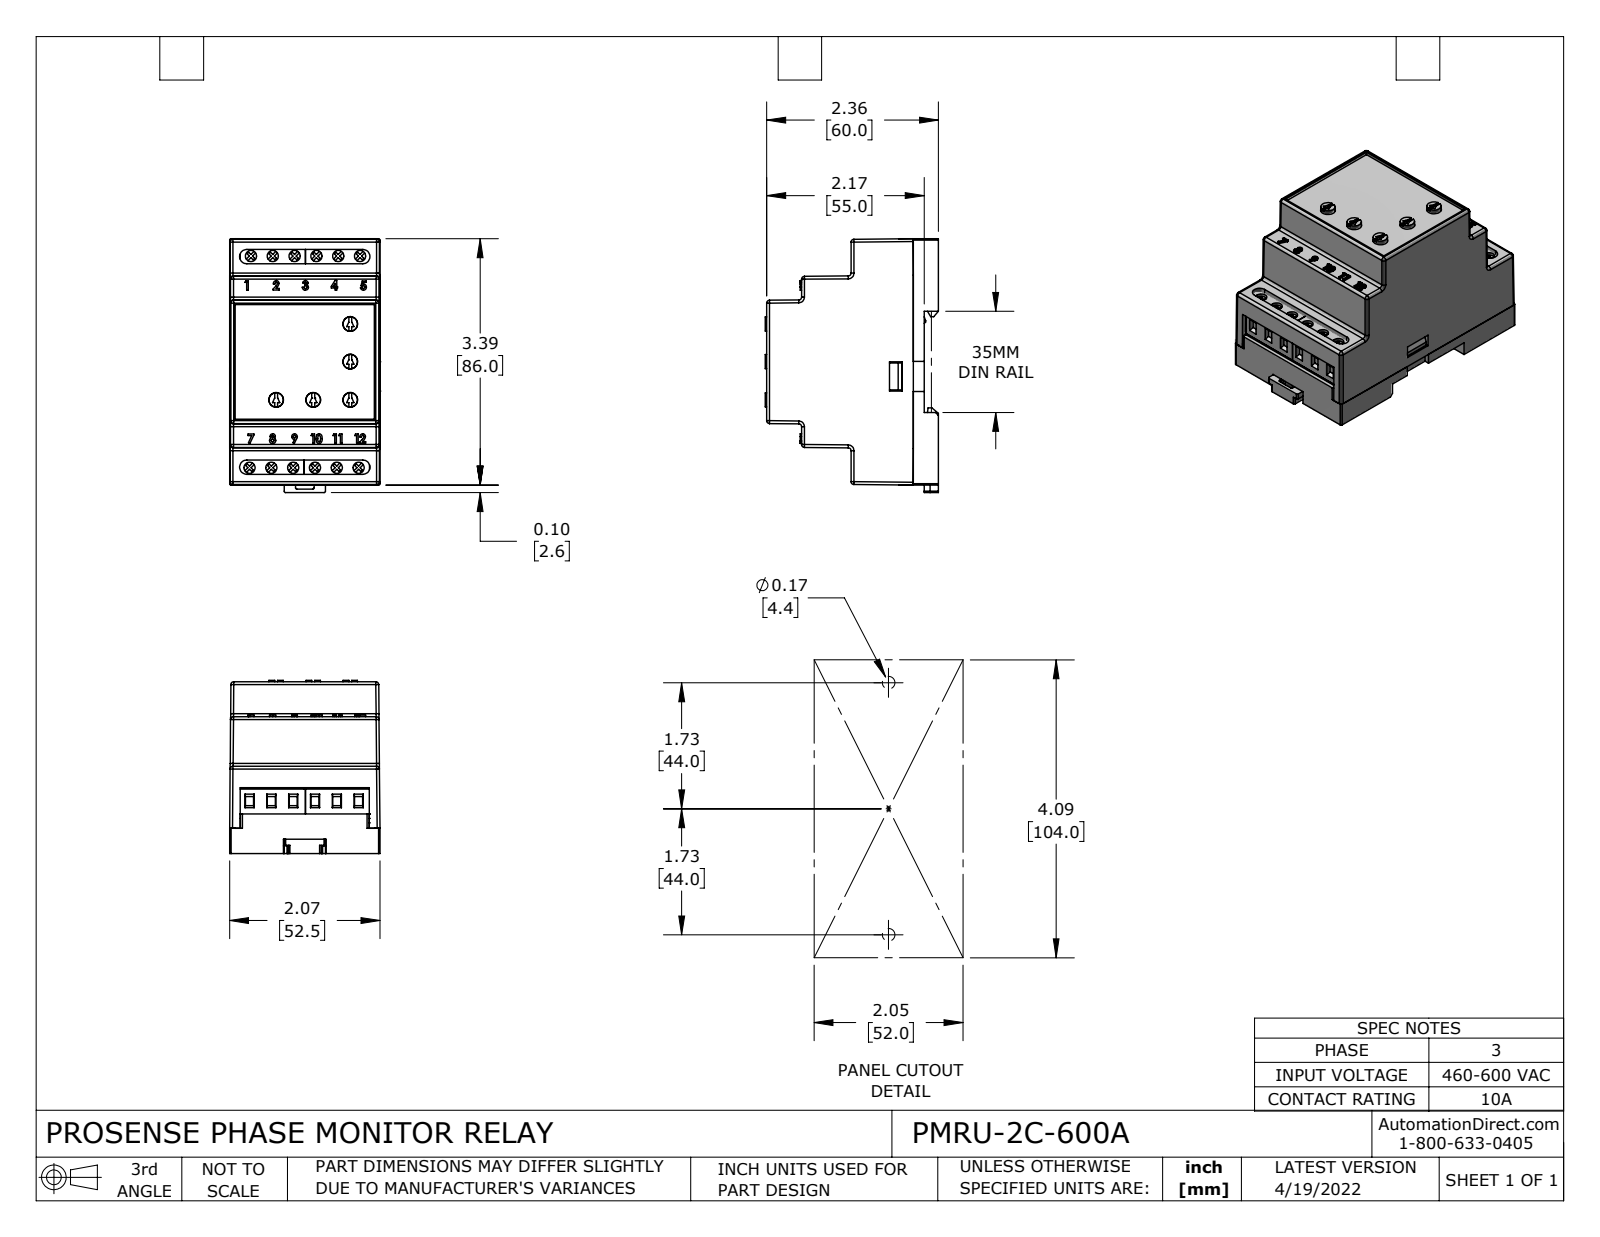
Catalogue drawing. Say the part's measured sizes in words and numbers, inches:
The part is named "PMRU-2C-600A". Its 3-D file was written by "SolidWorks 2021 (CONFIG_CONTROL_DESIGN)". It is 13 solids with 1220 faces: 891 planar, 206 cylindrical and 123 other. Overall it measures 3.489 by 2.382 by 2.067 inches. Its volume is 3.469 cubic inches and its surface area 99.03 square inches. Round holes: 12 of diameter 0.154, 5 of diameter 0.203. Round bosses or shafts: 5 of diameter 0.197, 2 of diameter 0.148, 1 of diameter 0.091, 1 of diameter 0.087. Partial cylindrical surfaces (rounded edges, fillets, slot ends): 40 of radius 0.01, 36 of radius 0.02, 28 of radius 0.039, 16 of radius 0.021, 4 of radius 0.02, 4 of radius 0.03, 4 of radius 0.098, 2 of radius 0.01. The main face-to-face distances are 0.059, 0.285, 0.062, 0.347, 0.094, 0.191, 0.253, 2.067, 0.079, 2.126. The hole center spacings are 0.3, 0.6, 0.9, 2.909, 2.923, 2.927, 1.2, 2.967.
